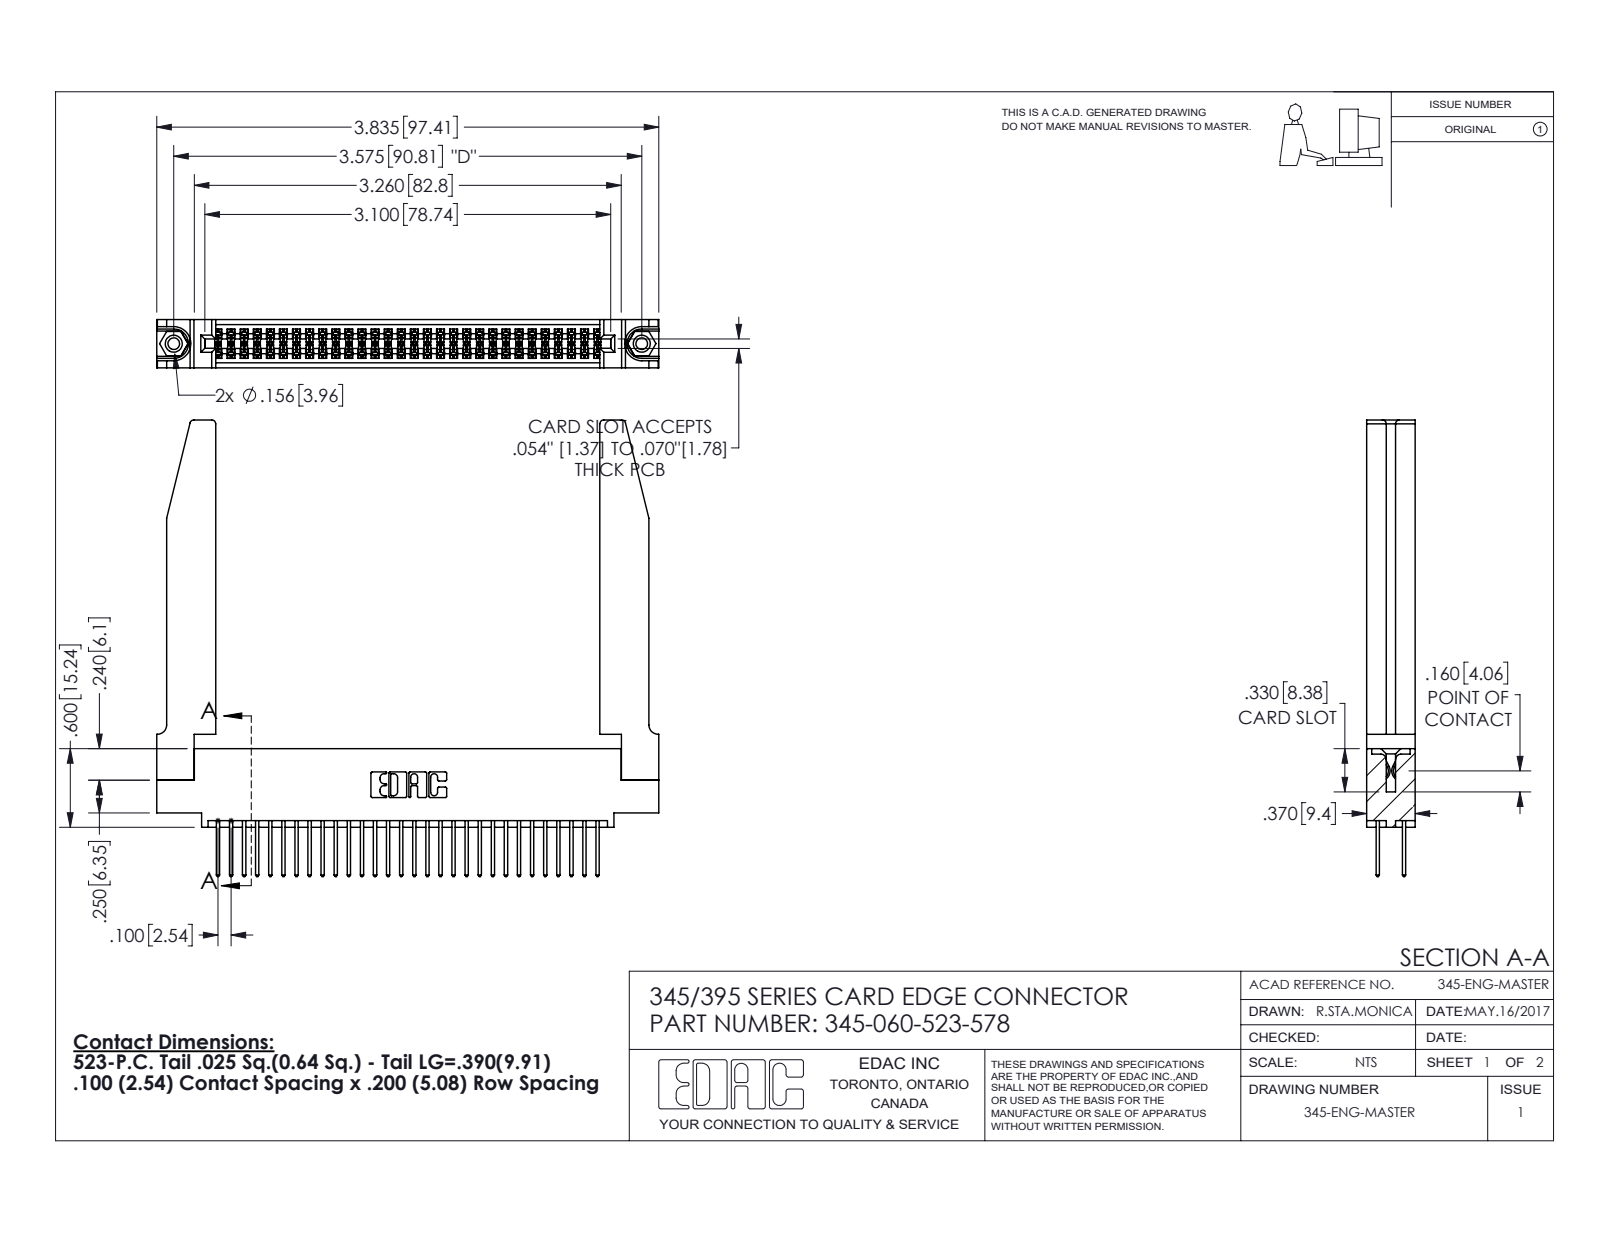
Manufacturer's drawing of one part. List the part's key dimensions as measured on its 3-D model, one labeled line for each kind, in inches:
Part name (STEP PRODUCT): 345-292-001_345-293-123; 345 Part_0.110 Offset - 0.156 Dia-TH; 345-220-078_345-220-078; 345-060-523-578 (+1 more)
STEP written by: SolidWorks 2016 (CONFIG_CONTROL_DESIGN)
Units: inches
Bodies: 65 solids, 3364 faces (2206 planar, 1106 cylindrical, 52 other)
Overall size (bounding box): 3.836 × 3.487 × 0.37
Volume: 1.048 in³ · Surface area: 32.78 in²
Round holes (diameter × count): ⌀0.089 ×2, ⌀0.125 ×2, ⌀0.156 ×2, ⌀0.064 ×1
Round bosses / shafts (diameter × count): ⌀0.155 ×2
Partial cylindrical surfaces — rounded edges, fillets, slot ends (radius × count): R0.006 ×90, R0.01 ×60, R0.01 ×22, R0.03 ×8, R0.007 ×6, R0.031 ×6, R0.026 ×3, R0.014 ×2
Main face-to-face distances: 0.37, 0.072, 0.298, 0.2, 0.098, 0.272, 0.025, 0.225, 0.175, 0.148
Hole centre spacings: 0.27, 3.34, 3.575
